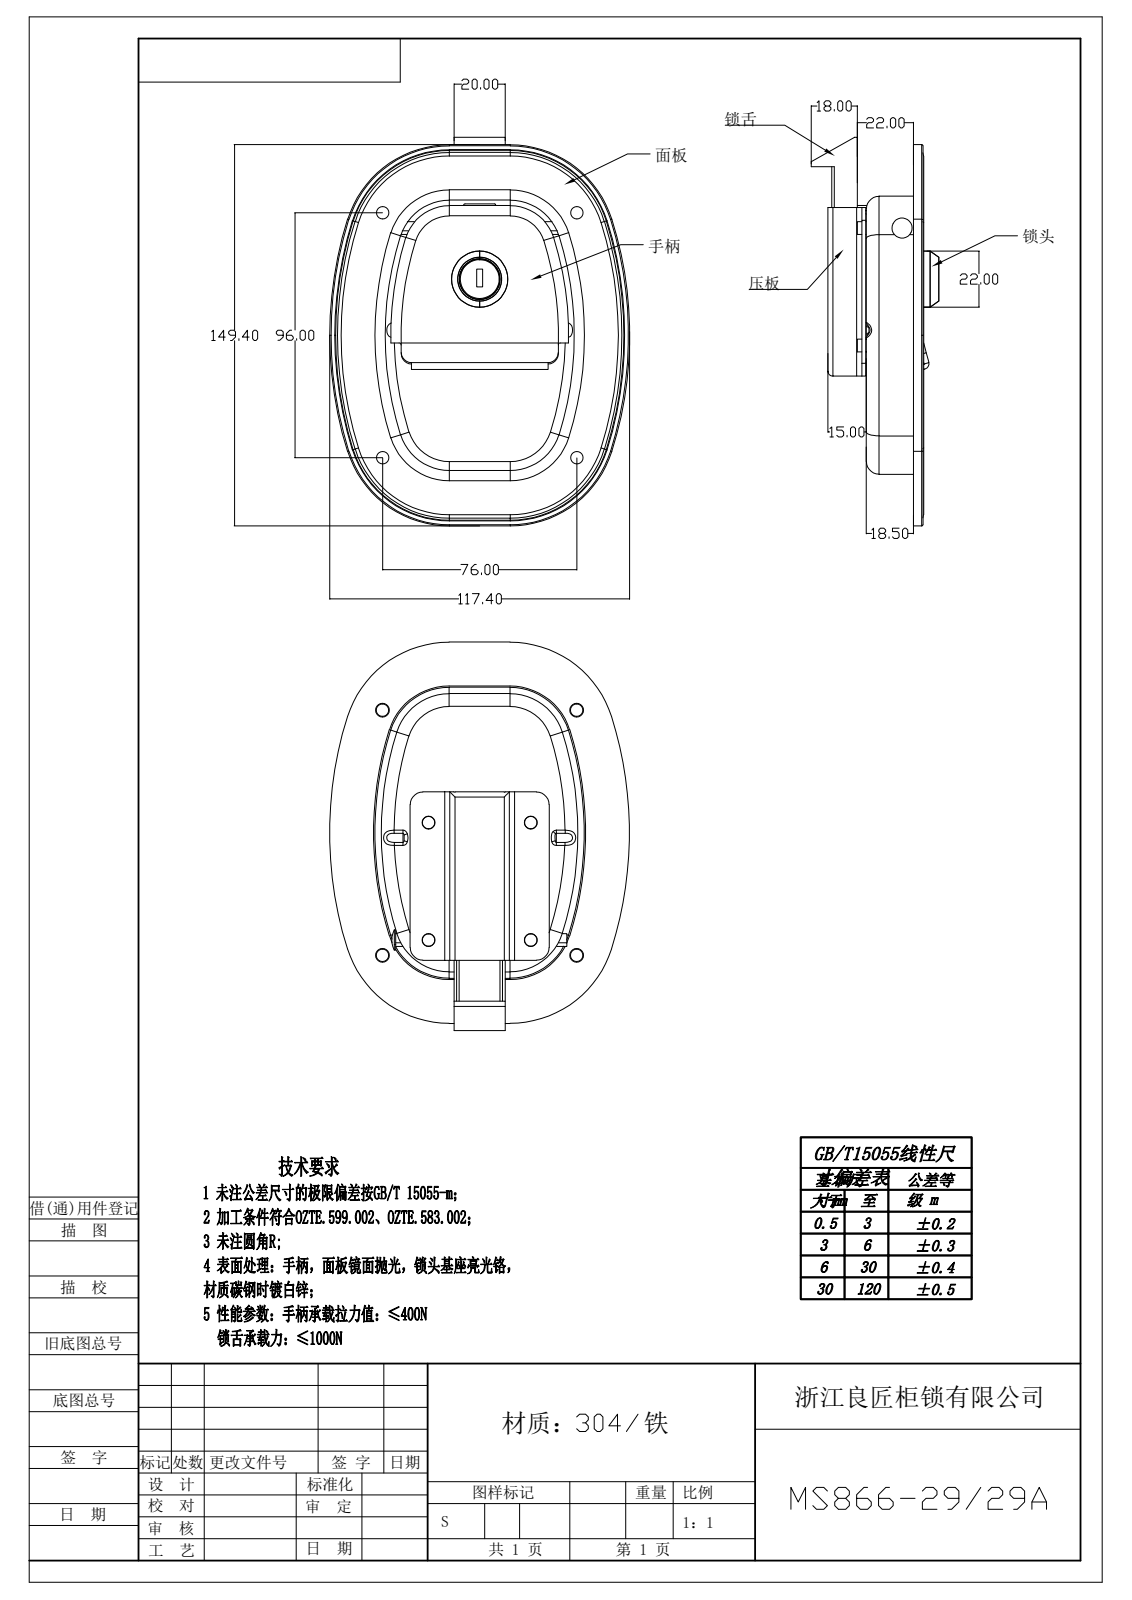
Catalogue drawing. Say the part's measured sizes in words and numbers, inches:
The part is named "图块 01". Its 3-D file was written by "Rhino 8.5 (CONFIG_CONTROL_DESIGN)". It is 15 solids with 696 faces: 273 planar, 252 cylindrical and 171 other. Overall it measures 5.993 by 4.622 by 1.965 inches. Its volume is 3.804 cubic inches and its surface area 145.5 square inches. Round holes: 5 of diameter 0.197, 4 of diameter 0.201, 4 of diameter 0.217, 1 of diameter 0.039, 1 of diameter 0.157, 1 of diameter 0.598, 1 of diameter 0.63. Round bosses or shafts: 4 of diameter 0.256, 4 of diameter 0.197, 1 of diameter 0.866, 1 of diameter 0.622, 1 of diameter 0.315, 1 of diameter 0.063. Partial cylindrical surfaces (rounded edges, fillets, slot ends): 17 of radius 0.02, 14 of radius 0.079, 10 of radius 0.059, 9 of radius 0.118, 8 of radius 0.039, 6 of radius 0.197, 5 of radius 0.138, 5 of radius 0.157. The main face-to-face distances are 0.059, 0.827, 0.098, 0.079, 0.157, 0.886, 0.669, 0.768, 0.728, 0.067. The hole center spacings are 0.747, 1.113, 1.291, 1.575, 1.811, 1.813, 1.872, 2.167.
